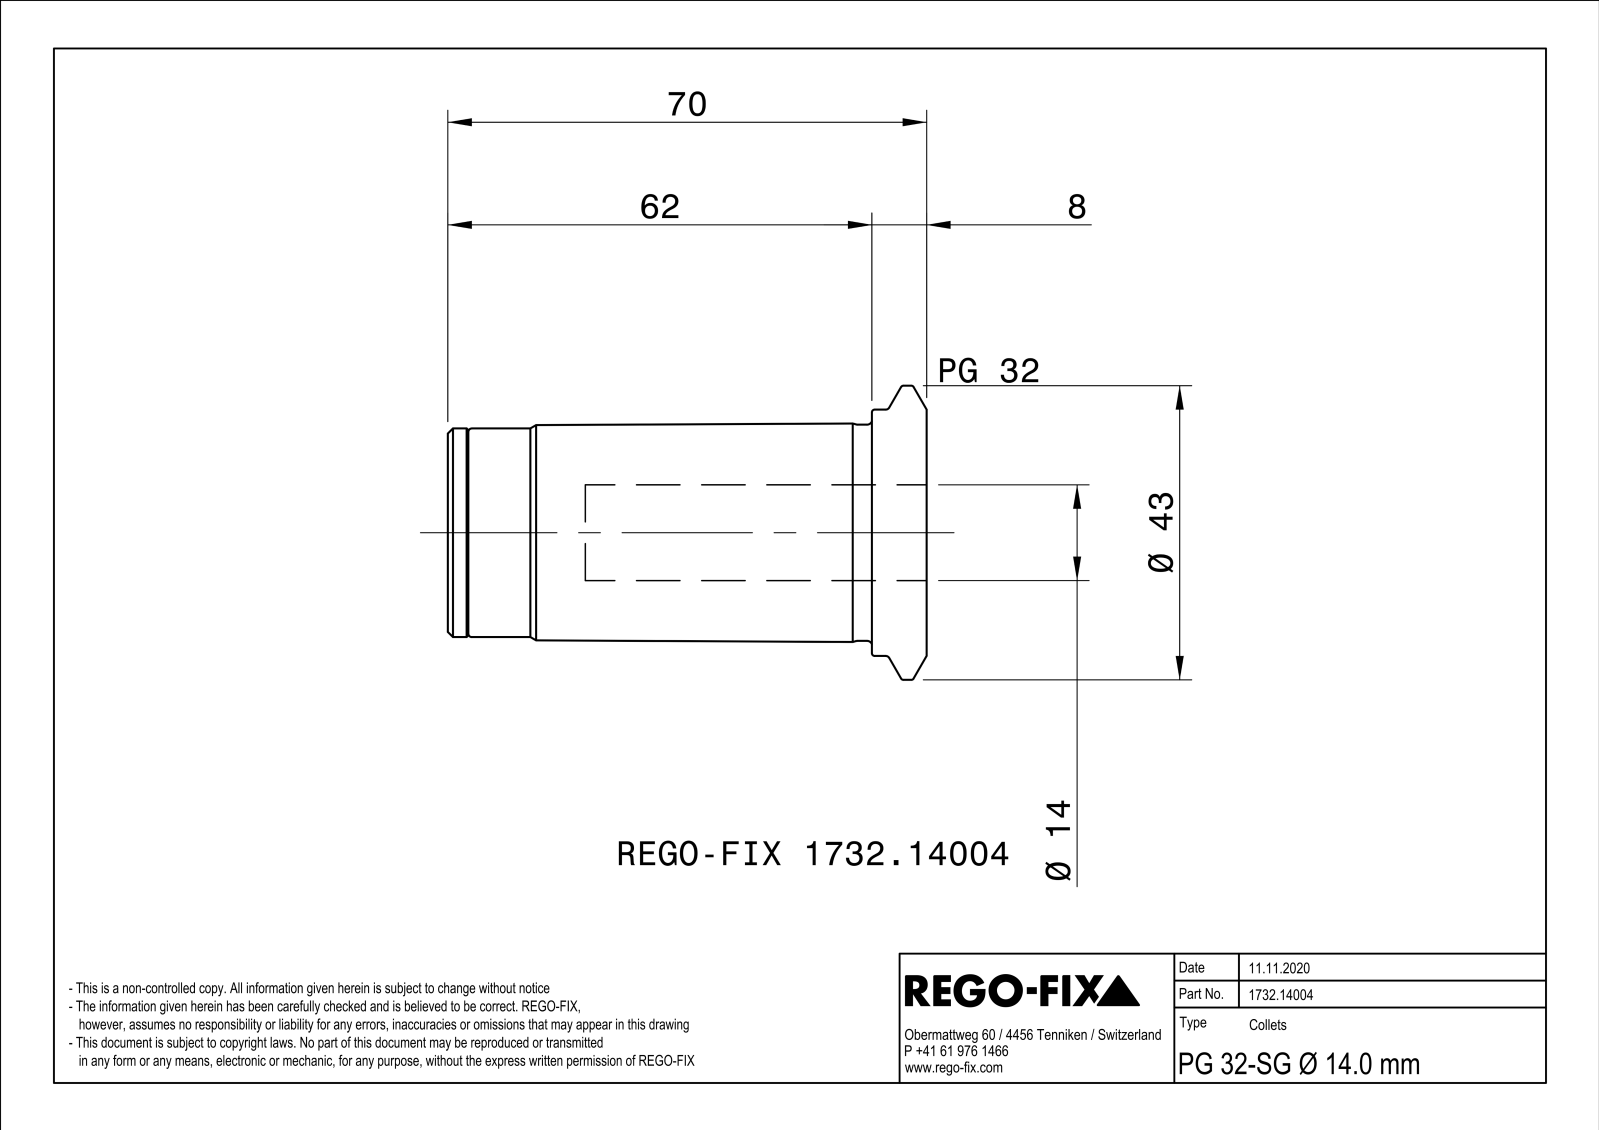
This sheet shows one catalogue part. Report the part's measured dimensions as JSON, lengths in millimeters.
{"part_name": "NOCUT", "step_written_by": "SIEMENS PLM Software Solid Edge ST10 (AUTOMOTIVE_DESIGN)", "units": "millimeters", "bodies": {"solids": 1, "faces": 127, "planar": 31, "cylindrical": 41, "other": 55}, "overall_size": [70, 43, 42.99], "volume_mm3": 43896, "surface_area_mm2": 16560, "round_holes": [[4, 3], [8.92, 1], [10.5, 1], [14, 1], [15.5, 1], [26.92, 1], [28.5, 1]], "round_bosses_or_shafts": [[43, 1], [36, 1], [31.6, 1], [30.5, 1], [26.5, 1], [21, 1]], "partial_cylinders_radius": [[2, 6], [3.5, 3], [3.98, 1], [4.75, 1], [8.75, 1]], "face_to_face_distances": [1, 70, 58, 12, 59, 11, 8, 60, 2, 10], "hole_center_spacings": [7.75, 13.42, 13.43]}
